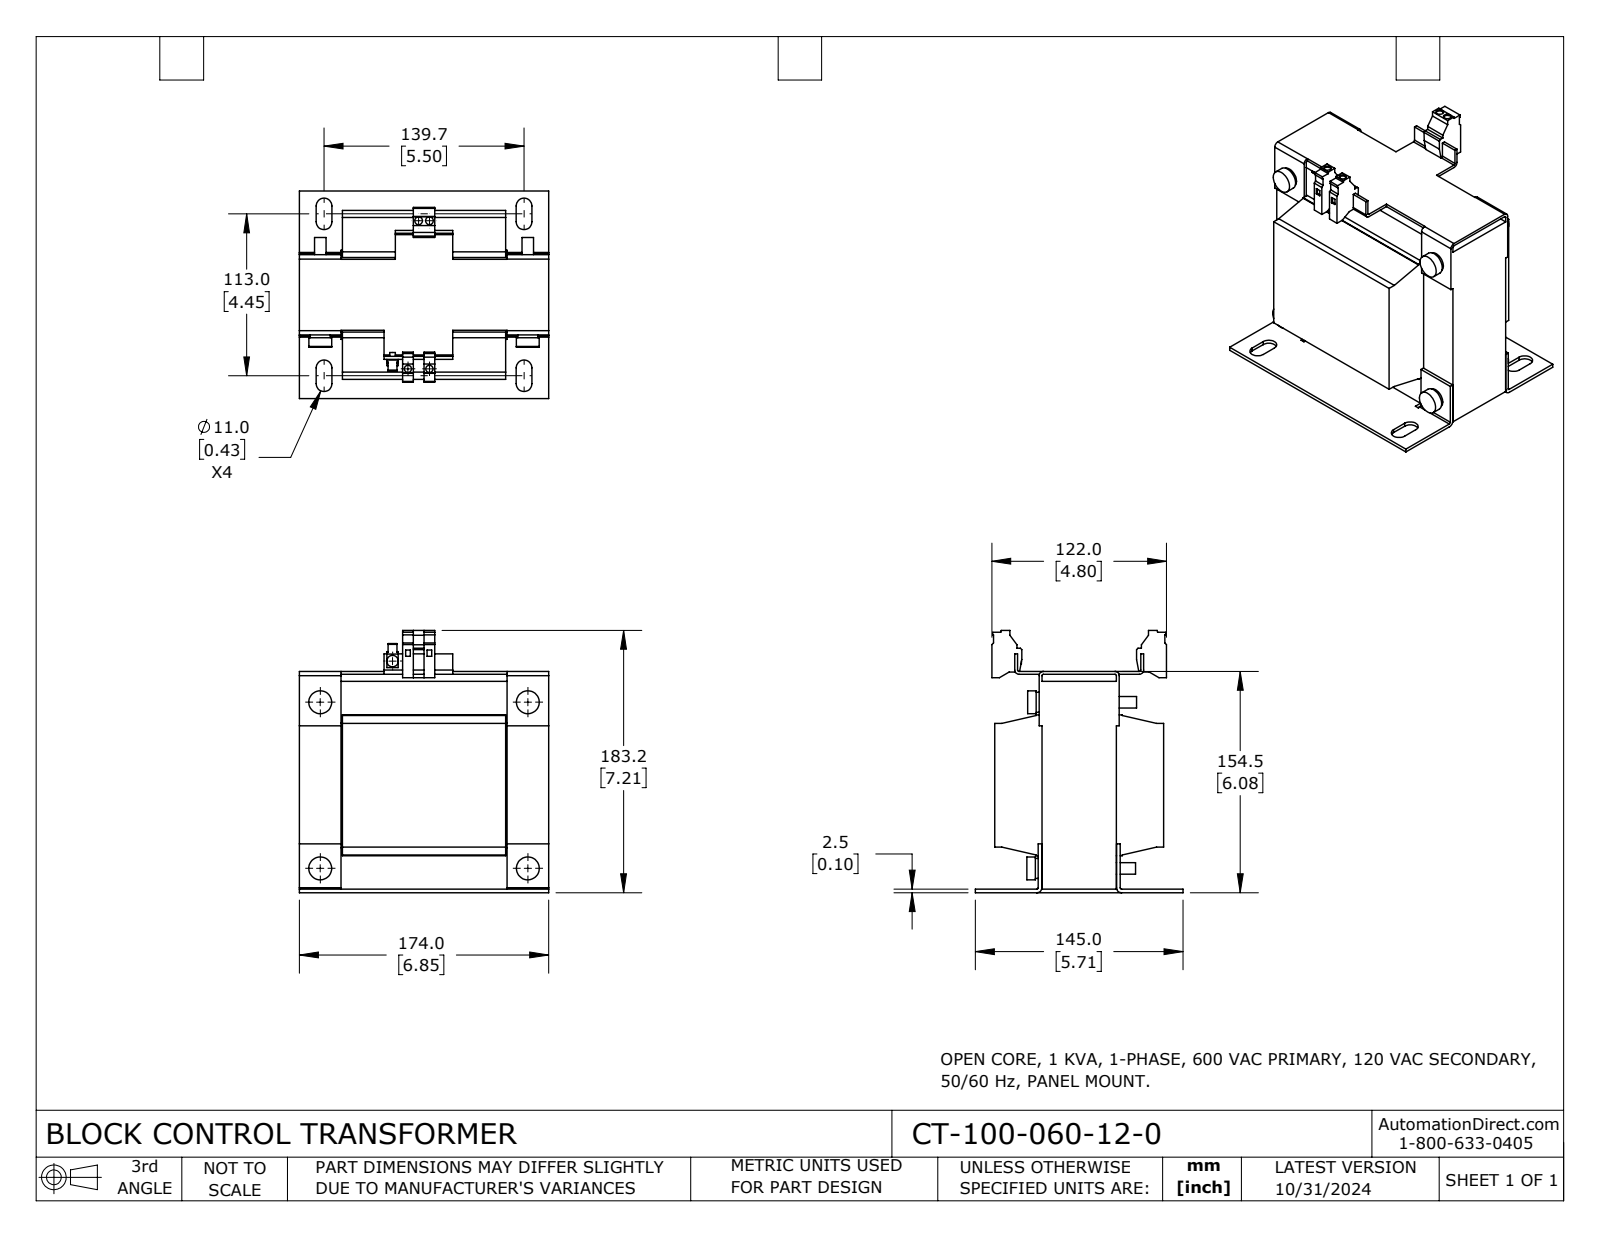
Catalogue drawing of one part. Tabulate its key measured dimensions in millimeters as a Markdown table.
| quantity | value |
| --- | --- |
| part name | CT-100-060-12-0 |
| STEP written by | SolidWorks 2023 (CONFIG_CONTROL_DESIGN) |
| units | millimeters |
| bodies | 1 solid, 320 faces (239 planar, 81 cylindrical, 0 other) |
| overall size | 183.2 × 174 × 145 |
| volume | 2 109 000 mm³ |
| surface area | 213 500 mm² |
| round holes (diameter × count) | 5 × 2, 5.4 × 2 |
| round bosses / shafts (diameter × count) | 8 × 5, 16 × 4, 14 × 4, 10 × 2, 4 × 1 |
| partial cylindrical surfaces (radius × count) | 5.5 × 8, 1 × 6, 3 × 4, 3.5 × 2 |
| main face-to-face distances | 2.5, 33, 85, 145, 30, 144, 29, 2, 52, 116 |
| hole center spacings | 103.7, 7.5, 15, 103.4, 104.5 |
